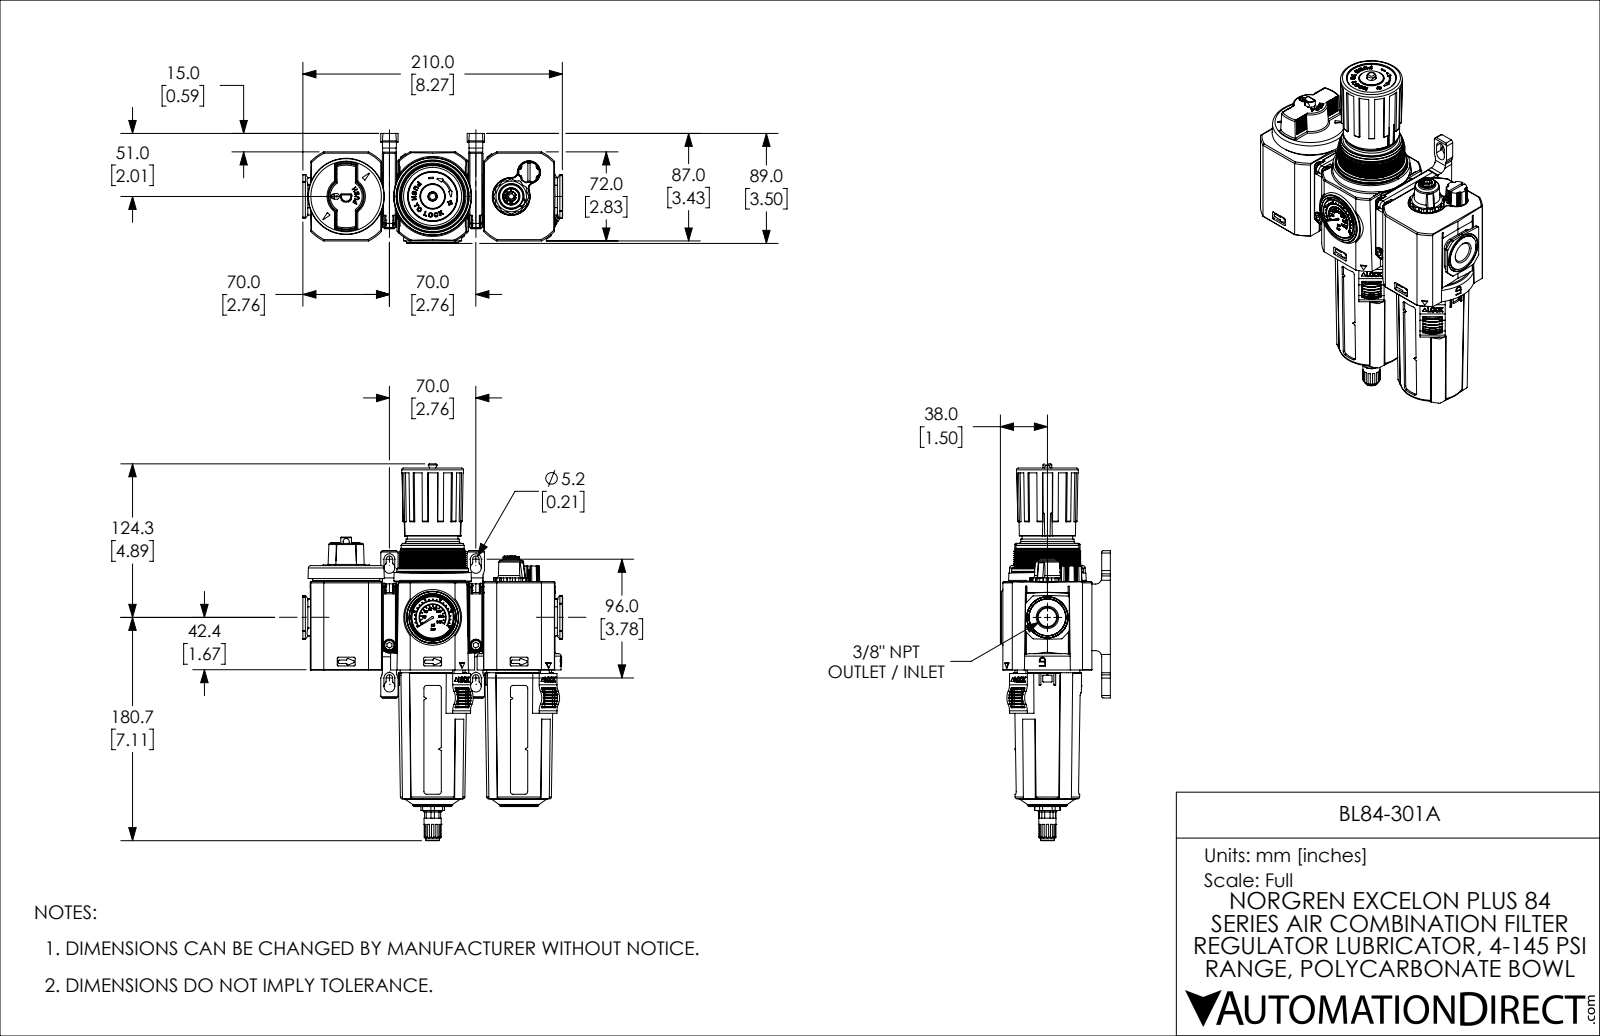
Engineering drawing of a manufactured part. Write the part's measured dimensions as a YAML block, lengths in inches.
part_name: "BL84-301A"
step_written_by: "SolidWorks 2021 (CONFIG_CONTROL_DESIGN)"
units: inches
bodies: {solids: 18, faces: 5076, planar: 2136, cylindrical: 2078, other: 862}
overall_size: [12.005, 8.278, 3.504]
volume: 92.04
surface_area: 530.1
round_holes:
  - {diameter: 0.22, count: 3}
  - {diameter: 0.163, count: 2}
  - {diameter: 0.177, count: 2}
  - {diameter: 0.197, count: 2}
  - {diameter: 0.335, count: 2}
  - {diameter: 0.969, count: 2}
  - {diameter: 2.461, count: 2}
  - {diameter: 0.039, count: 1}
  - {diameter: 0.059, count: 1}
  - {diameter: 0.126, count: 1}
  - {diameter: 0.246, count: 1}
  - {diameter: 0.268, count: 1}
round_bosses_or_shafts:
  - {diameter: 0.197, count: 4}
  - {diameter: 0.394, count: 2}
  - {diameter: 0.335, count: 2}
  - {diameter: 0.327, count: 2}
  - {diameter: 0.299, count: 2}
  - {diameter: 0.157, count: 2}
  - {diameter: 2.283, count: 1}
  - {diameter: 2.119, count: 1}
partial_cylinders:
  - {radius: 0.039, count: 110}
  - {radius: 0.03, count: 74}
  - {radius: 0.02, count: 65}
  - {radius: 0.01, count: 51}
  - {radius: 0.079, count: 44}
  - {radius: 0.028, count: 32}
  - {radius: 0.004, count: 30}
  - {radius: 0.012, count: 27}
face_to_face_distances: [2.756, 5.512, 0.226, 2.835, 0.404, 2.411, 2.913, 2.815, 0.059, 2.376]
hole_center_spacings: [2.756, 0.157, 0.522, 0.856, 0.886, 1.027, 1.378, 1.638]
